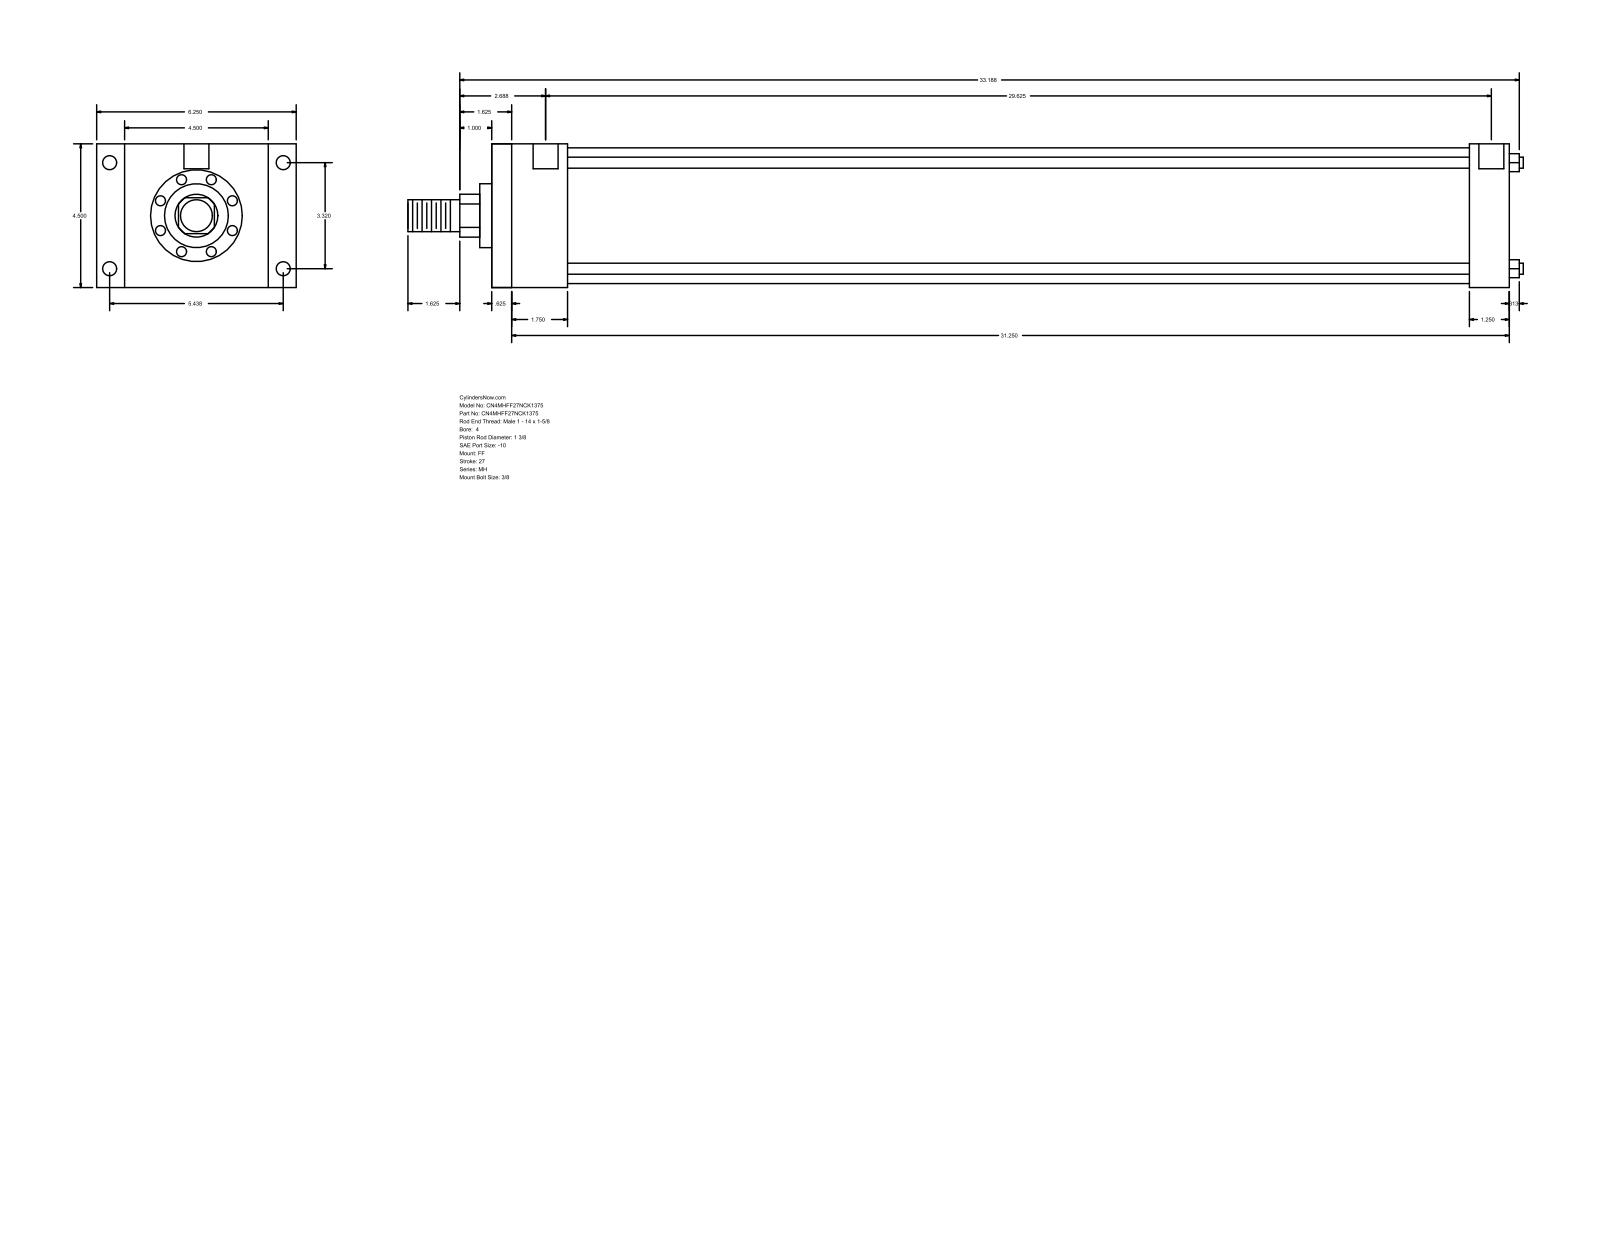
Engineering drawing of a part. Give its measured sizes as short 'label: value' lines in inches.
name: MH_FF__0400_1.375
written by: GSSL Pune (CONFIG_CONTROL_DESIGN)
unit: in
bodies: 0 solids, 92 faces (64 planar, 28 cylindrical, 0 other)
size: 34.937 × 6.25 × 4.5
holes: 4× ⌀0.344, 4× ⌀0.438, 2× ⌀0.781
bosses: 4× ⌀0.345, 1× ⌀4.25, 1× ⌀2, 1× ⌀1.375, 1× ⌀1
rounds: 1× R0.672
face distances: 4.5, 31.875, 0.625, 31.25, 2.375, 1.75, 29.5, 30.625, 30, 28.25
hole spacings: 0.063, 3.32, 5.438, 6.371, 29.688, 29.75, 29.625
